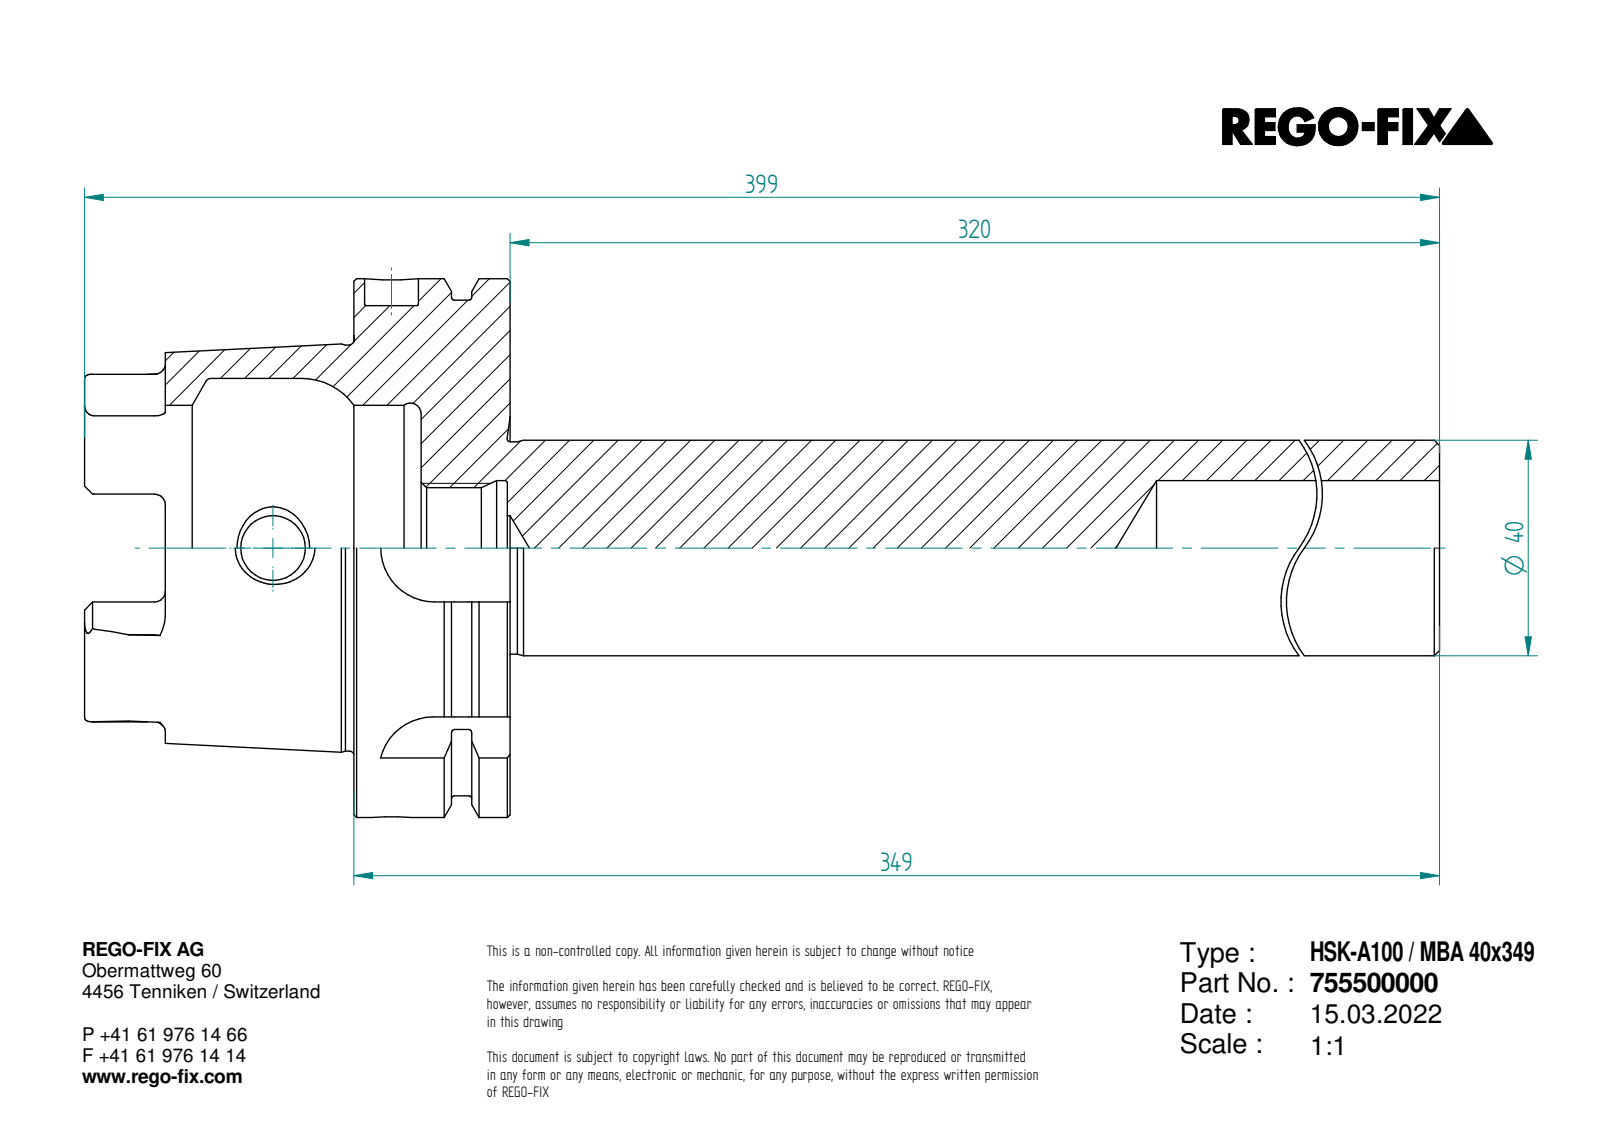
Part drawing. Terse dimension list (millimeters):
name: 0025831
written by: ST-DEVELOPER v16.7 (AUTOMOTIVE_DESIGN)
unit: mm
bodies: 1 solid, 150 faces (49 planar, 42 cylindrical, 59 other)
size: 399 × 100 × 100
volume: 548 968 mm³; area: 104 588 mm²
holes: 2× ⌀12, 1× ⌀7.5, 1× ⌀10, 1× ⌀22.38, 1× ⌀25, 1× ⌀53, 1× ⌀63
bosses: 1× ⌀100, 1× ⌀92, 1× ⌀75.36, 1× ⌀40, 1× ⌀39.4
rounds: 8× R4.88, 6× R2, 2× R10, 1× R11
face distances: 29, 12.5, 16.5, 35, 47.5, 64, 384, 349, 336.5, 320
